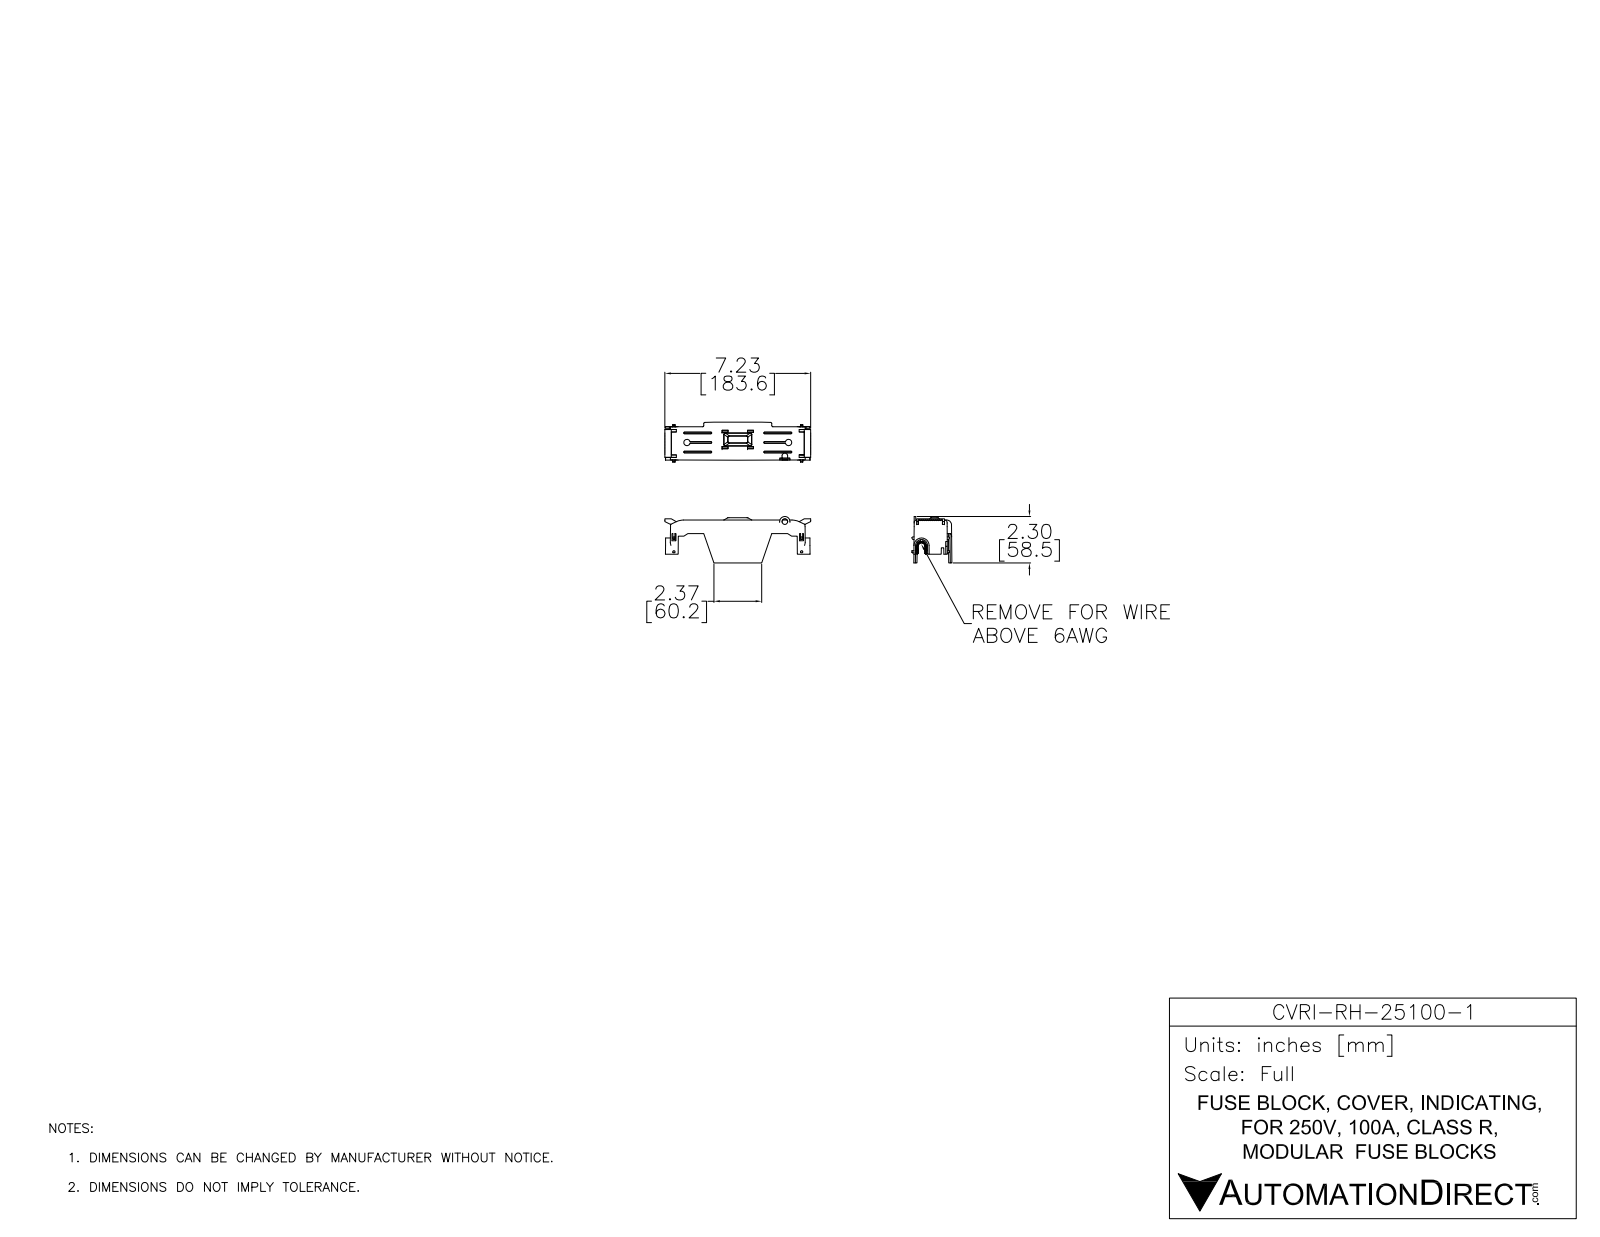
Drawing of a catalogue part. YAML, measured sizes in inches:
part_name: "CVRI-RH-25100-1"
step_written_by: "SolidWorks 2017 (AUTOMOTIVE_DESIGN)"
units: inches
bodies: {solids: 1, faces: 1324, planar: 879, cylindrical: 102, other: 343}
overall_size: [7.229, 2.304, 1.983]
volume: 3.152
surface_area: 85.59
partial_cylinders:
  - {radius: 0.039, count: 18}
  - {radius: 0.118, count: 14}
  - {radius: 0.031, count: 6}
  - {radius: 0.059, count: 4}
  - {radius: 0.01, count: 2}
  - {radius: 0.02, count: 2}
  - {radius: 0.079, count: 2}
  - {radius: 0.138, count: 2}
face_to_face_distances: [0.079, 0.217, 0.138, 0.295, 0.567, 0.118, 0.197, 2.244, 0.346, 0.472]
